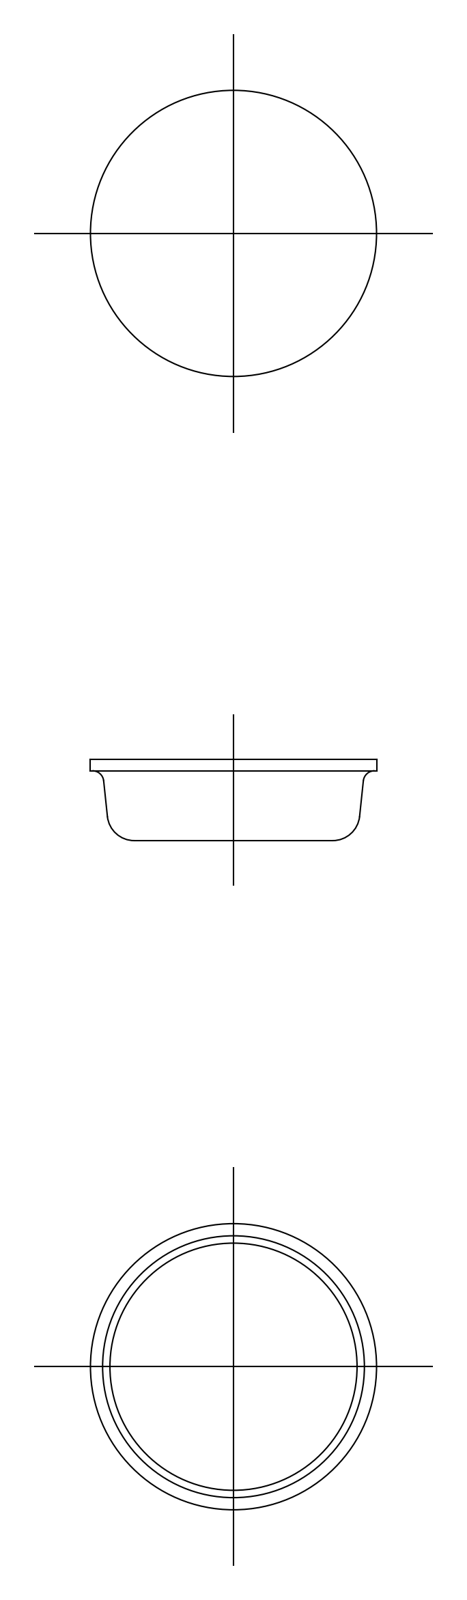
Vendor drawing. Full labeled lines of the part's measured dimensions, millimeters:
Part name (STEP PRODUCT): rubber foot
STEP written by: CADfix (AUTOMOTIVE_DESIGN)
Units: millimetres
Bodies: 1 solid, 11 faces (0 planar, 0 cylindrical, 11 other)
Overall size (bounding box): 12.7 × 12.7 × 3.6
Volume: 369 mm³ · Surface area: 352 mm²
